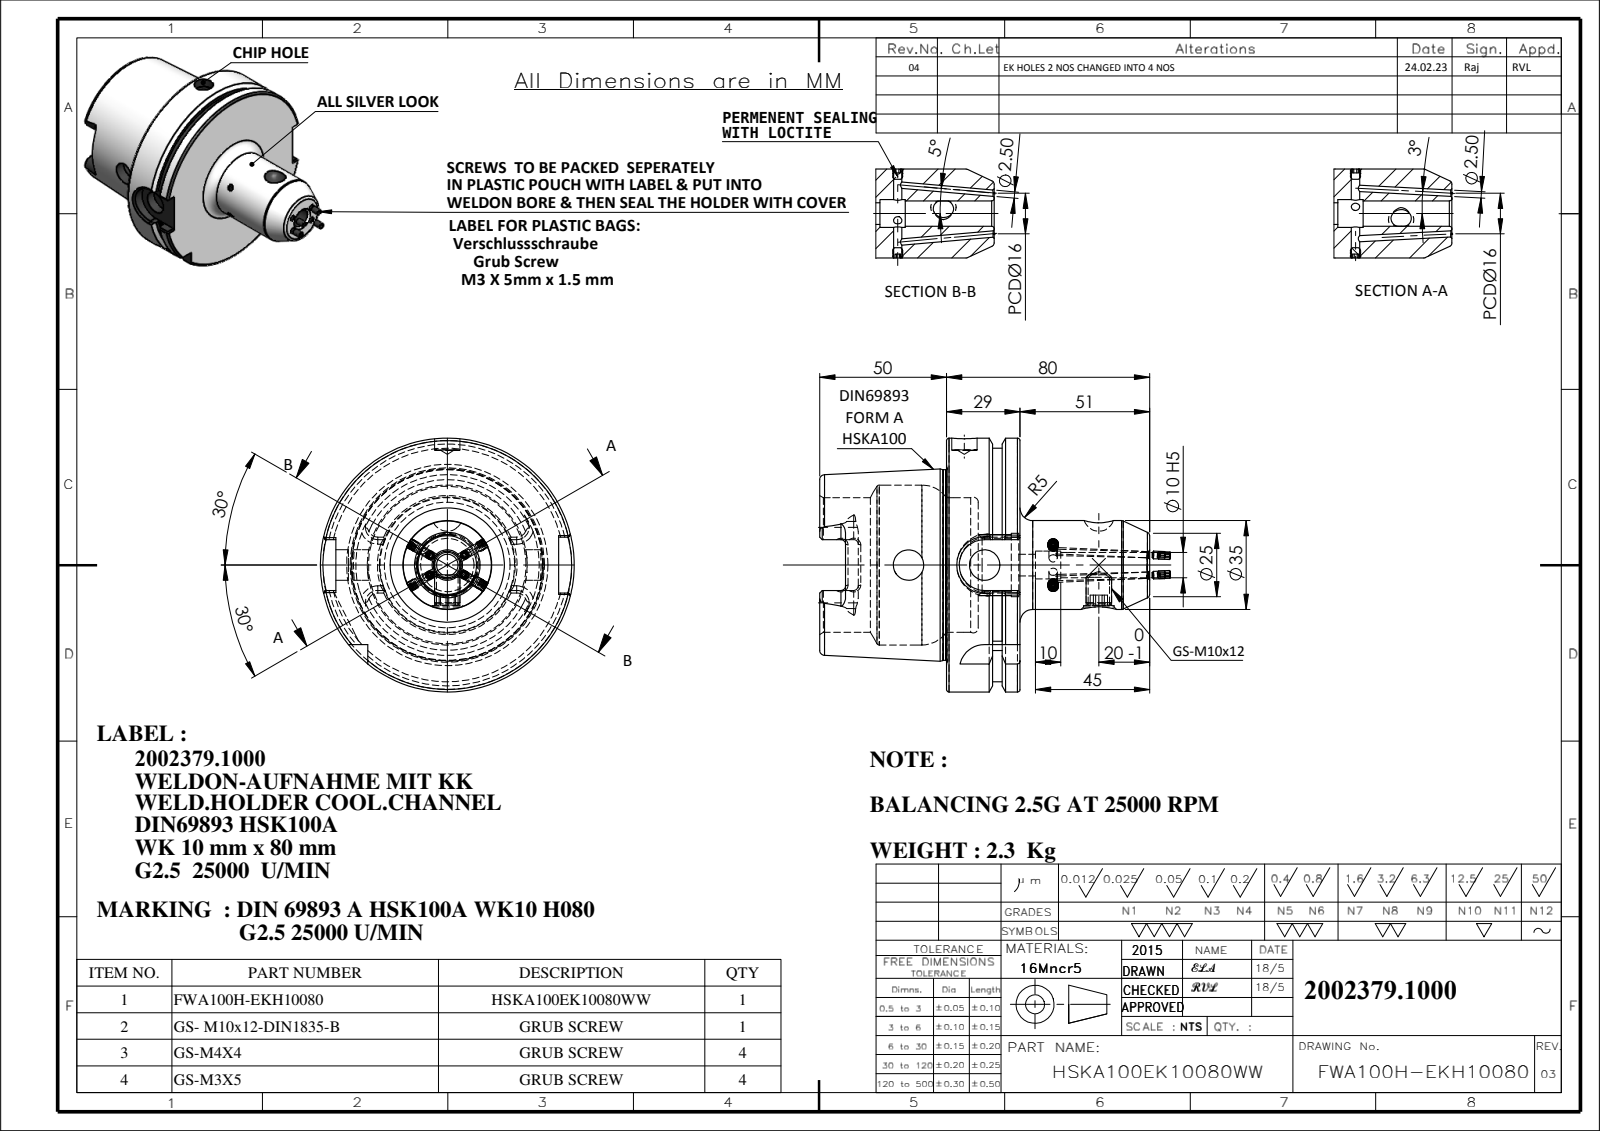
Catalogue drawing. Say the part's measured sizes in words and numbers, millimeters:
The part is named "GS-M4X4_DIN 913 - M4 x 4-N; GS-M10X12-DIN1835-B; HSKA100EK10080WW; 91100A-WK10080 (+1 more)". Its 3-D file was written by "SolidWorks 2018 (CONFIG_CONTROL_DESIGN)". It is 10 solids with 503 faces: 155 planar, 122 cylindrical and 226 other. Overall it measures 138.21 by 100 by 100 millimeters. Its volume is 295 520 cubic millimeters and its surface area 59 286 square millimeters. Round holes: 4 of diameter 2.5, 3 of diameter 12, 2 of diameter 3.3, 2 of diameter 8.5, 2 of diameter 10, 1 of diameter 11, 1 of diameter 21, 1 of diameter 25, 1 of diameter 53, 1 of diameter 63. Round bosses or shafts: 4 of diameter 3, 2 of diameter 4, 1 of diameter 100, 1 of diameter 92, 1 of diameter 75.16, 1 of diameter 35, 1 of diameter 10. Partial cylindrical surfaces (rounded edges, fillets, slot ends): 6 of radius 1.8, 4 of radius 4.88, 2 of radius 10, 1 of radius 11. The main face-to-face distances are 28.95, 12.5, 16.45, 50, 62.5, 78.95, 78.5, 28.5, 16, 0.45. The hole center spacings are 30, 53.
